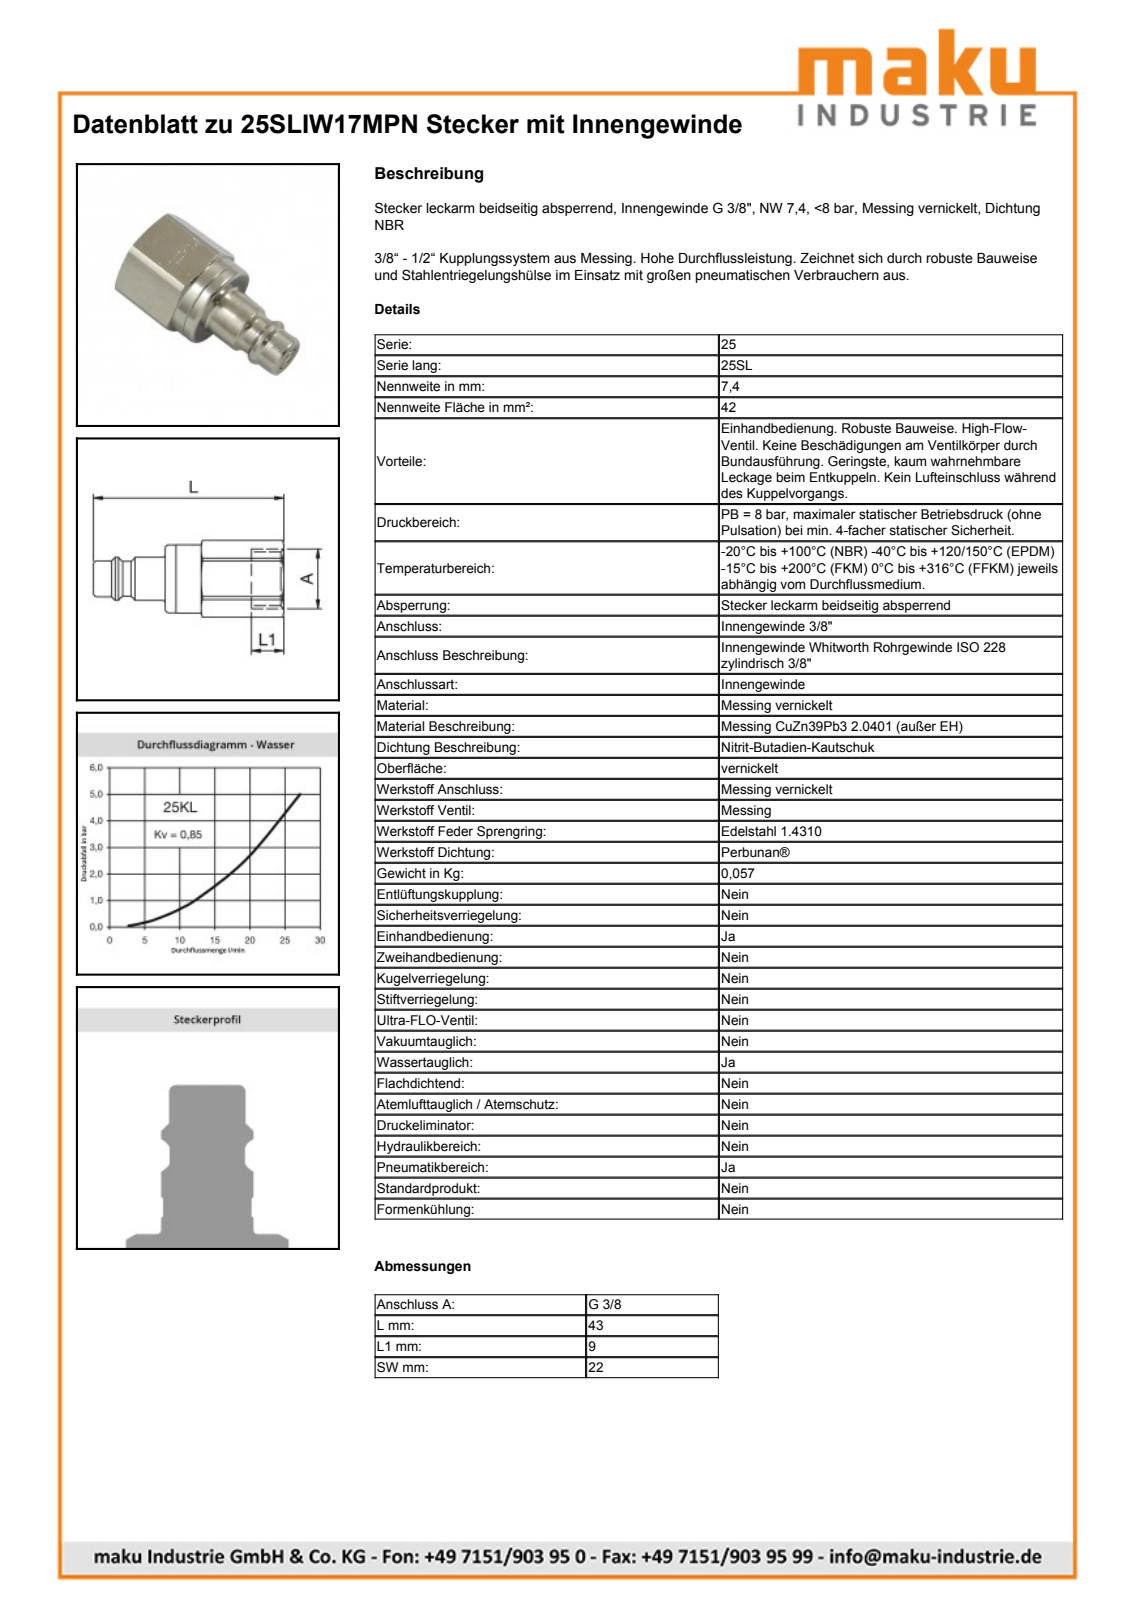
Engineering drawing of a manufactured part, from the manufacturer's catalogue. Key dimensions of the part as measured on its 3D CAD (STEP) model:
Part name (STEP PRODUCT): D112163
STEP written by: Autodesk Inventor 2013 (AUTOMOTIVE_DESIGN)
Units: millimetres
Bodies: 1 solid, 62 faces (15 planar, 21 cylindrical, 26 other)
Overall size (bounding box): 53 × 21.4 × 19.11
Volume: 9 890 mm³ · Surface area: 5 078 mm²
Round holes (diameter × count): ⌀7.85 ×1, ⌀14 ×1, ⌀14.95 ×1, ⌀15.1 ×1, ⌀16 ×1
Round bosses / shafts (diameter × count): ⌀19 ×1, ⌀18.95 ×1, ⌀14.5 ×1, ⌀12 ×1, ⌀9.9 ×1, ⌀9.75 ×1
Partial cylindrical surfaces — rounded edges, fillets, slot ends (radius × count): R10.7 ×1
Main face-to-face distances: 19, 24, 33, 9, 20, 44, 53, 27.5, 7.5, 16.5
